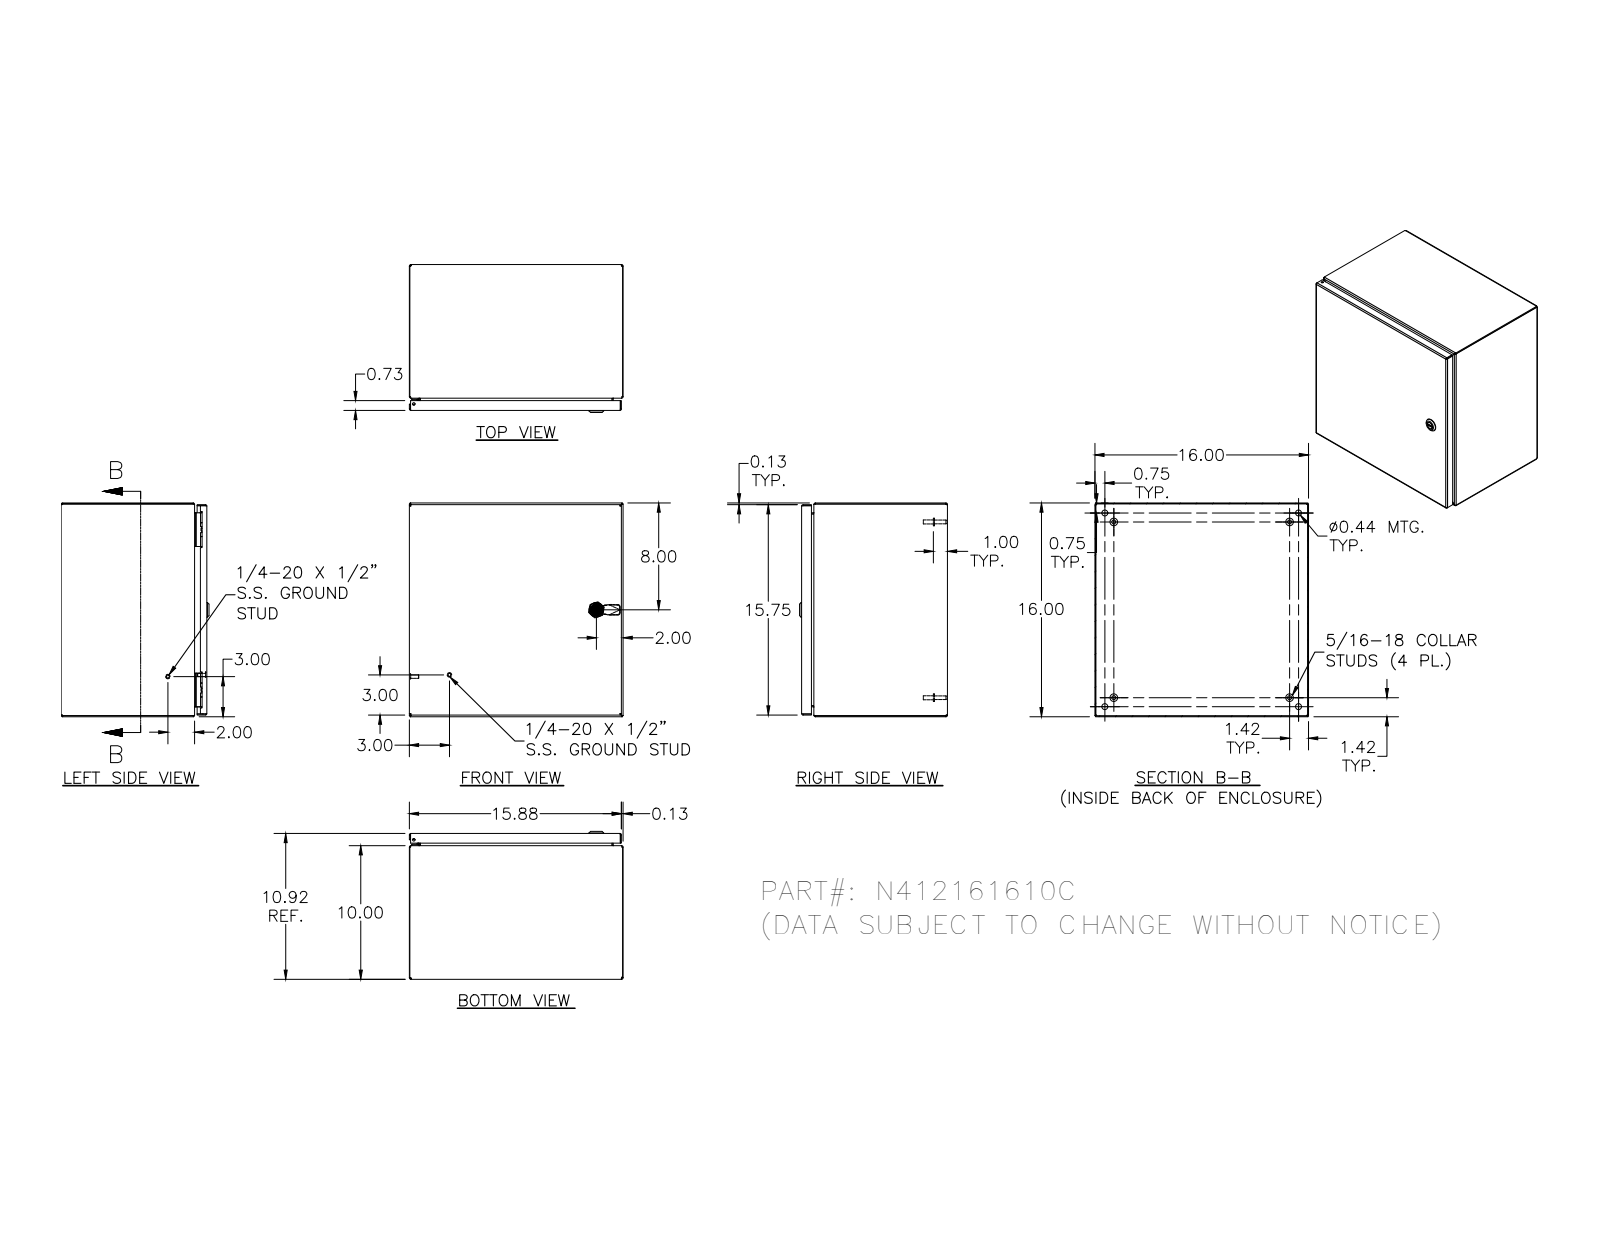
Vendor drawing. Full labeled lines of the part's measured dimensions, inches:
Part name (STEP PRODUCT): N412161610C
STEP written by: SolidWorks 2018 (AUTOMOTIVE_DESIGN)
Units: inches
Bodies: 33 solids, 1449 faces (530 planar, 547 cylindrical, 372 other)
Overall size (bounding box): 16 × 16 × 11.075
Volume: 95.14 in³ · Surface area: 2 589 in²
Round holes (diameter × count): ⌀0.188 ×5, ⌀0.093 ×4, ⌀0.152 ×4, ⌀0.167 ×4, ⌀0.172 ×4, ⌀0.437 ×4, ⌀0.156 ×2, ⌀0.187 ×1, ⌀0.197 ×1, ⌀0.315 ×1, ⌀0.394 ×1, ⌀0.402 ×1
Round bosses / shafts (diameter × count): ⌀0.25 ×10, ⌀0.131 ×5, ⌀0.563 ×4, ⌀0.36 ×4, ⌀0.32 ×4, ⌀0.3 ×4, ⌀0.275 ×4, ⌀0.256 ×4
Partial cylindrical surfaces — rounded edges, fillets, slot ends (radius × count): R0.012 ×30, R0.031 ×30, R0.05 ×26, R0.105 ×20, R0.016 ×18, R0.125 ×16, R0.02 ×13, R0.032 ×8
Main face-to-face distances: 0.074, 10.843, 15.926, 15.852, 0.074, 15.926, 16, 10.769, 10.917, 0.917
Hole centre spacings: 12, 0.66, 0.656, 1.307, 1.965, 11.34, 11.996, 12.656
